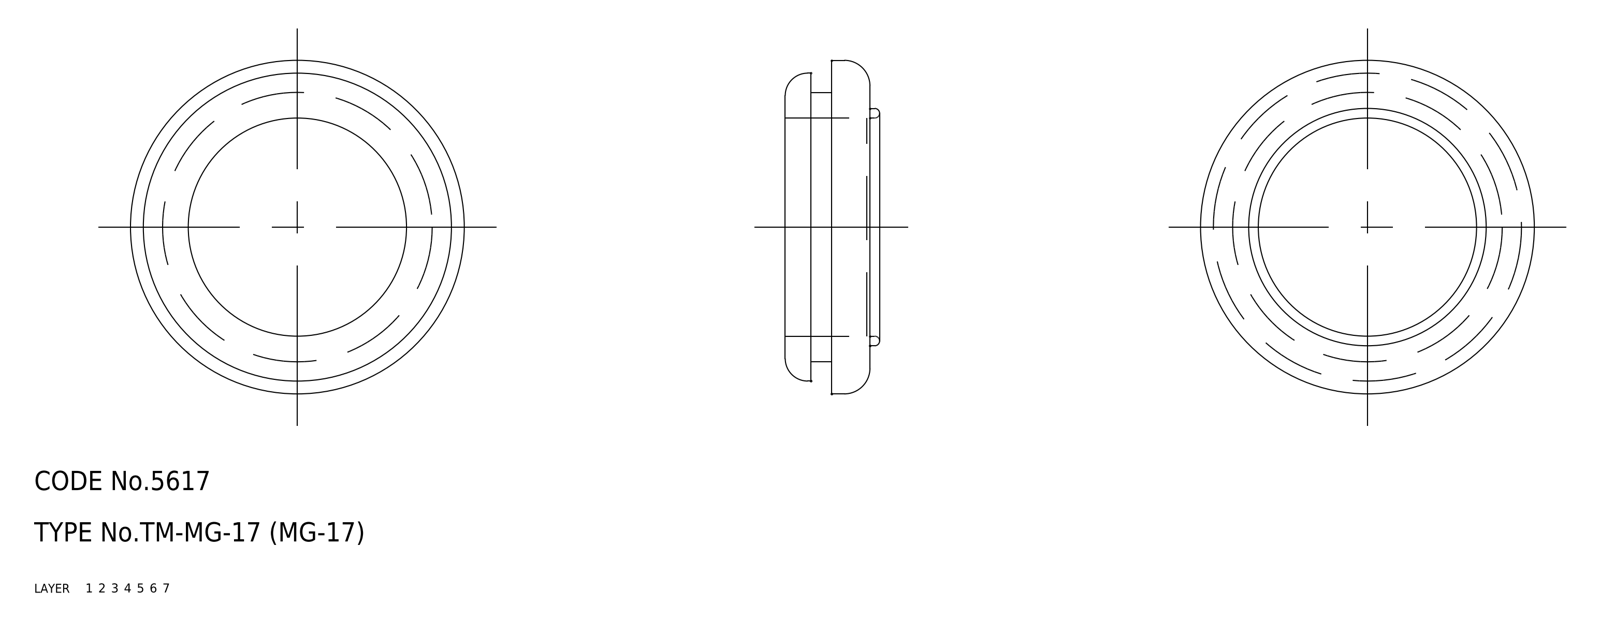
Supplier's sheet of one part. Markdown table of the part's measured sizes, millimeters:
| quantity | value |
| --- | --- |
| part name | grommet |
| STEP written by | CADfix (AUTOMOTIVE_DESIGN) |
| units | millimeters |
| bodies | 1 solid, 24 faces (0 planar, 0 cylindrical, 24 other) |
| overall size | 52 × 52 × 14.7 |
| volume | 12 204 mm³ |
| surface area | 8 205 mm² |
